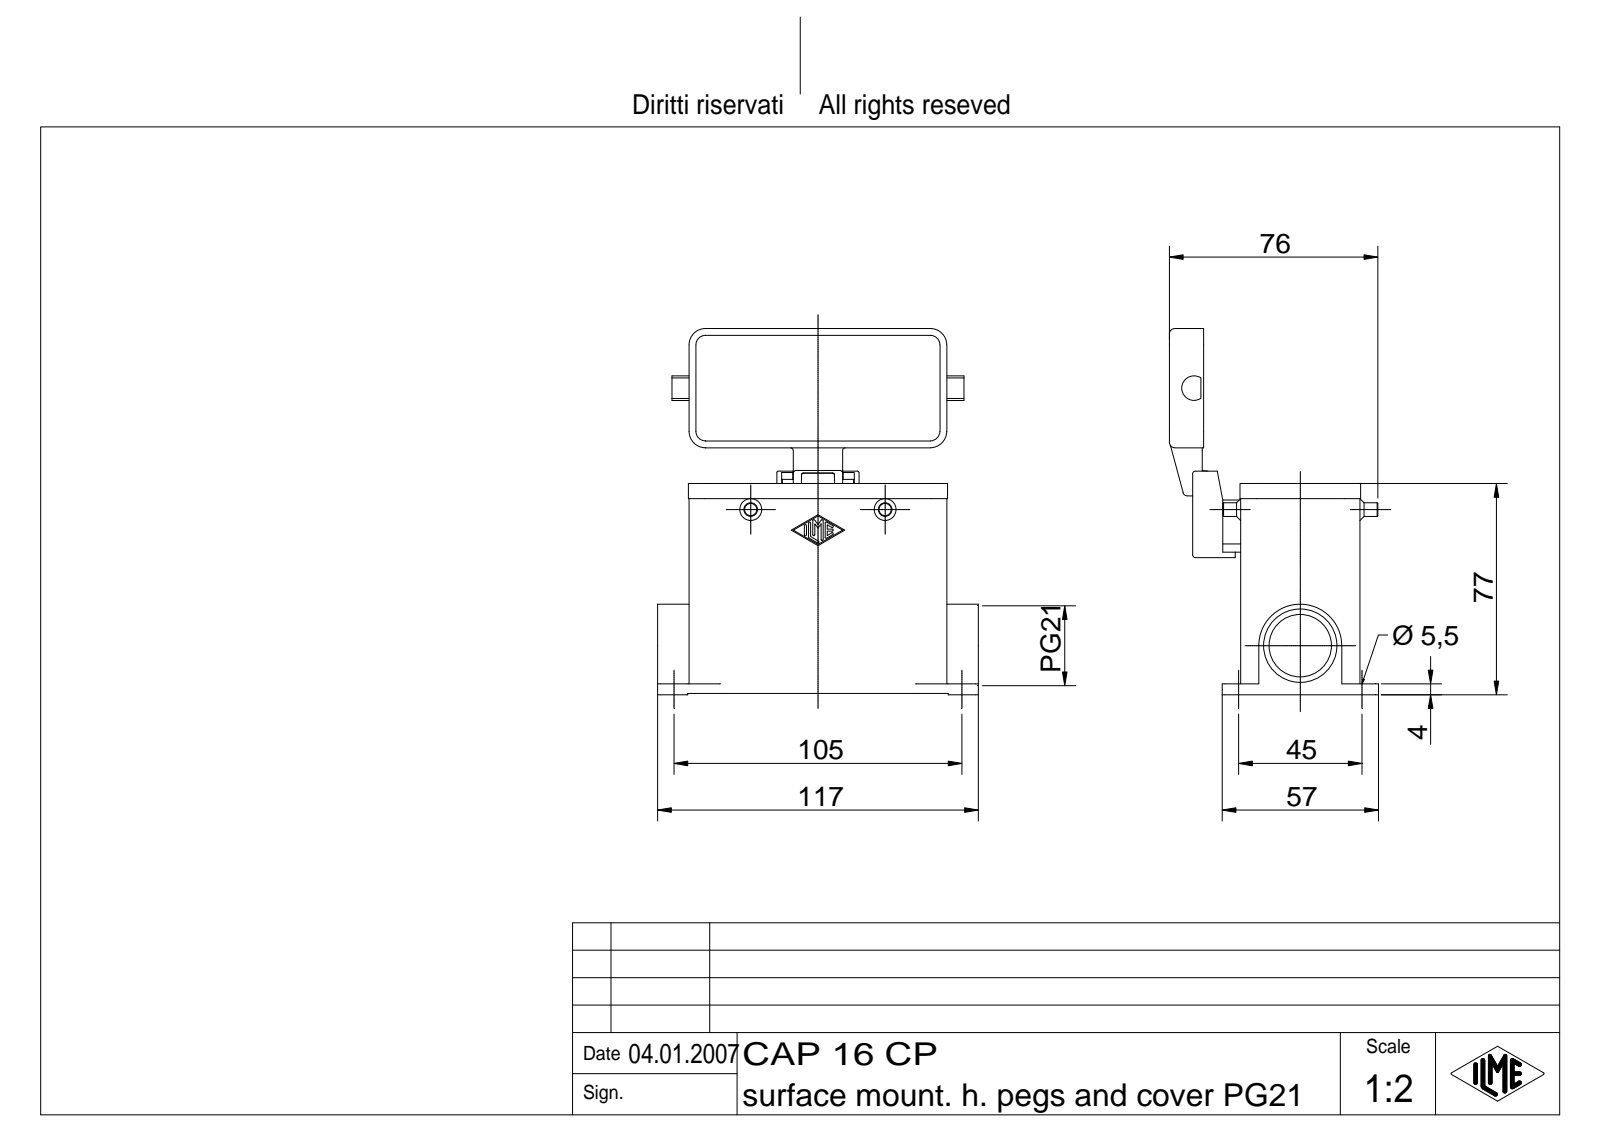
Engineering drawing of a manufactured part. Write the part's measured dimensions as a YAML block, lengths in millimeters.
part_name: "CAP 16 CP"
step_written_by: "Autodesk Inventor 7 (AUTOMOTIVE_DESIGN)"
units: millimeters
bodies: {solids: 2, faces: 471, planar: 173, cylindrical: 177, other: 121}
overall_size: [133.5, 117, 76.25]
volume: 136209
surface_area: 72907
round_holes:
  - {diameter: 5.5, count: 4}
  - {diameter: 4, count: 1}
  - {diameter: 5, count: 1}
  - {diameter: 22.78, count: 1}
  - {diameter: 26.78, count: 1}
round_bosses_or_shafts:
  - {diameter: 5, count: 2}
  - {diameter: 3, count: 2}
  - {diameter: 7, count: 1}
  - {diameter: 4, count: 1}
partial_cylinders:
  - {radius: 1, count: 26}
  - {radius: 0.38, count: 14}
  - {radius: 6, count: 12}
  - {radius: 0.5, count: 9}
  - {radius: 0.7, count: 8}
  - {radius: 2, count: 8}
  - {radius: 3, count: 4}
  - {radius: 3.5, count: 4}
face_to_face_distances: [3, 40.5, 43.5, 3.5, 37.5, 29, 22.5, 69.5, 66.5, 26]
hole_center_spacings: [45, 105, 114.24]
